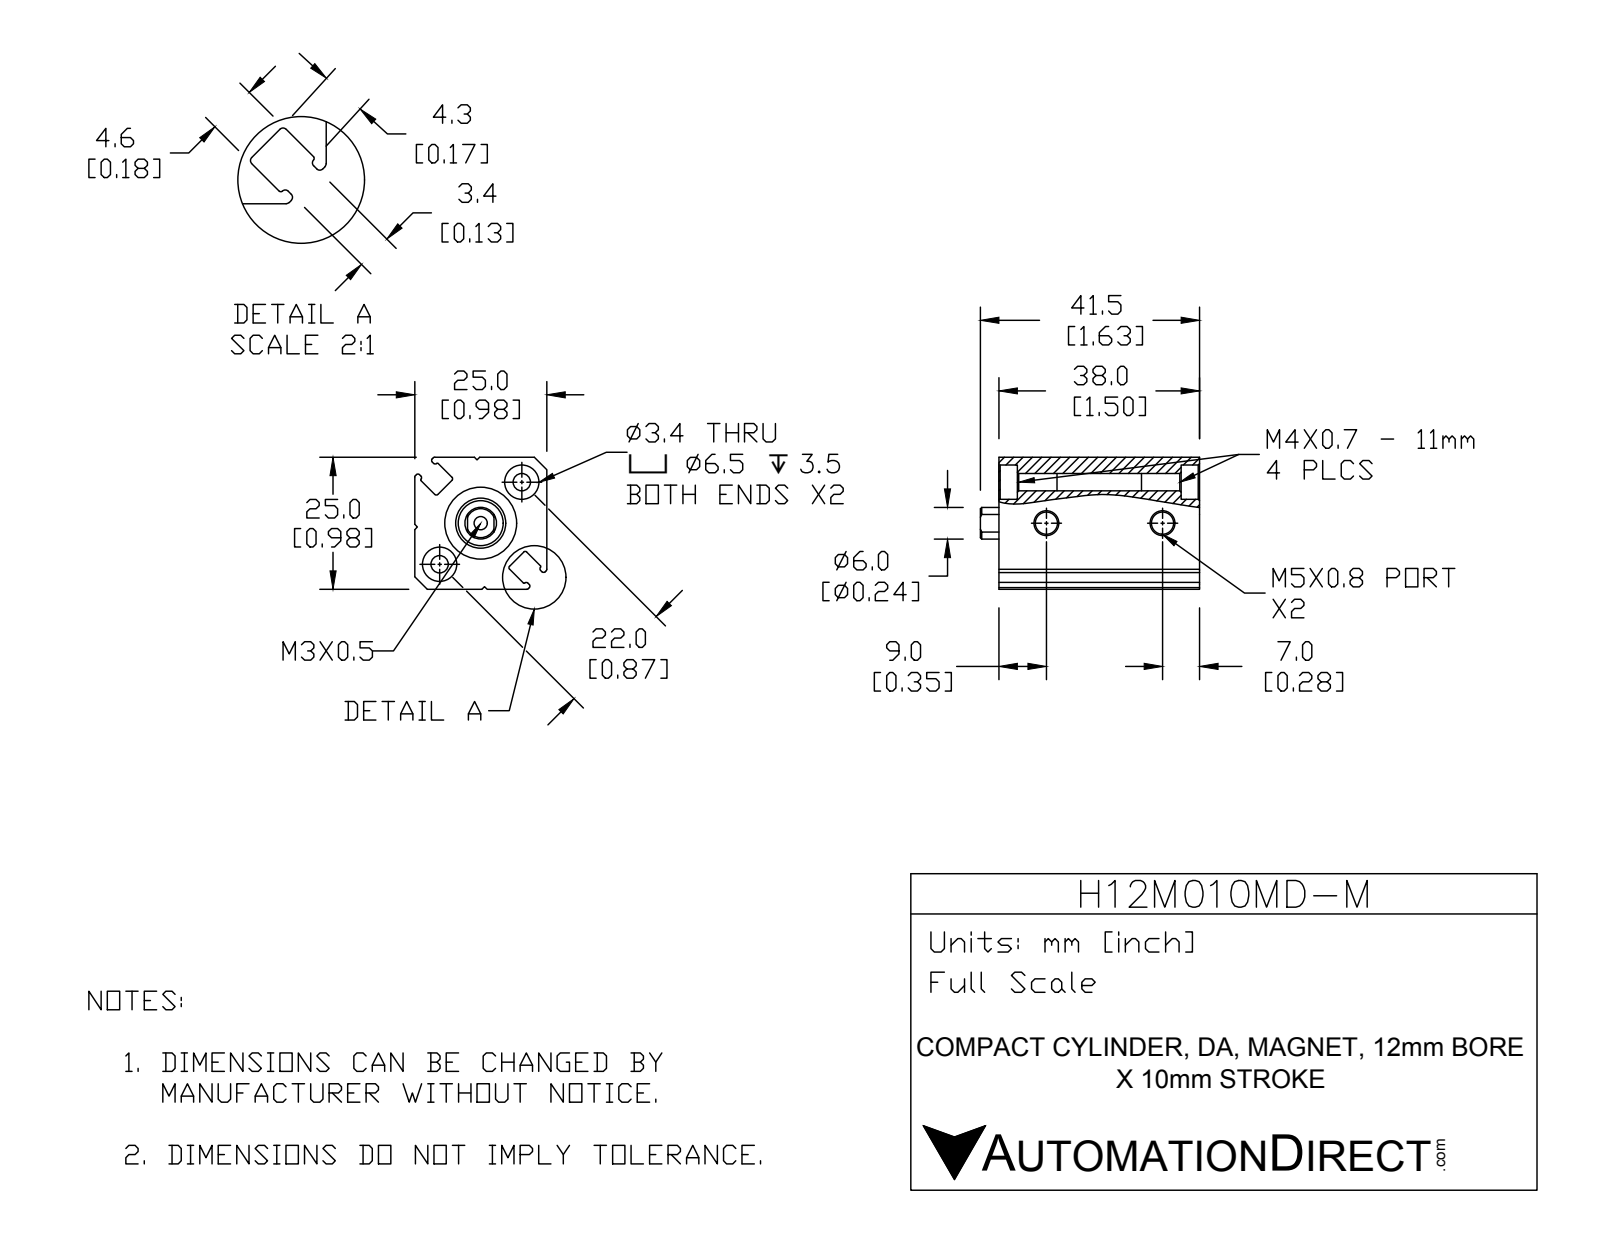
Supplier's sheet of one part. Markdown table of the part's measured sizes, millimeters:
| quantity | value |
| --- | --- |
| part name | H12M010MD-M-PISTON; H12M010MD-M-BODY; H12M010MD-M |
| STEP written by | SolidWorks 2015 (CONFIG_CONTROL_DESIGN) |
| units | millimeters |
| bodies | 2 solids, 128 faces (49 planar, 54 cylindrical, 25 other) |
| overall size | 41.5 × 25 × 25 |
| volume | 19 003 mm³ |
| surface area | 9 183 mm² |
| round holes (diameter × count) | 3.3 × 2, 4.2 × 2, 6.5 × 2, 2.5 × 1, 6 × 1, 12 × 1, 13.6 × 1 |
| round bosses / shafts (diameter × count) | 9.5 × 1 |
| partial cylindrical surfaces (radius × count) | 0.4 × 16, 0.2 × 4 |
| main face-to-face distances | 25, 38, 4.6, 5.5, 13.7, 18.3, 32.5, 32, 19.2, 17.7 |
| hole center spacings | 11, 22, 22.01 |
